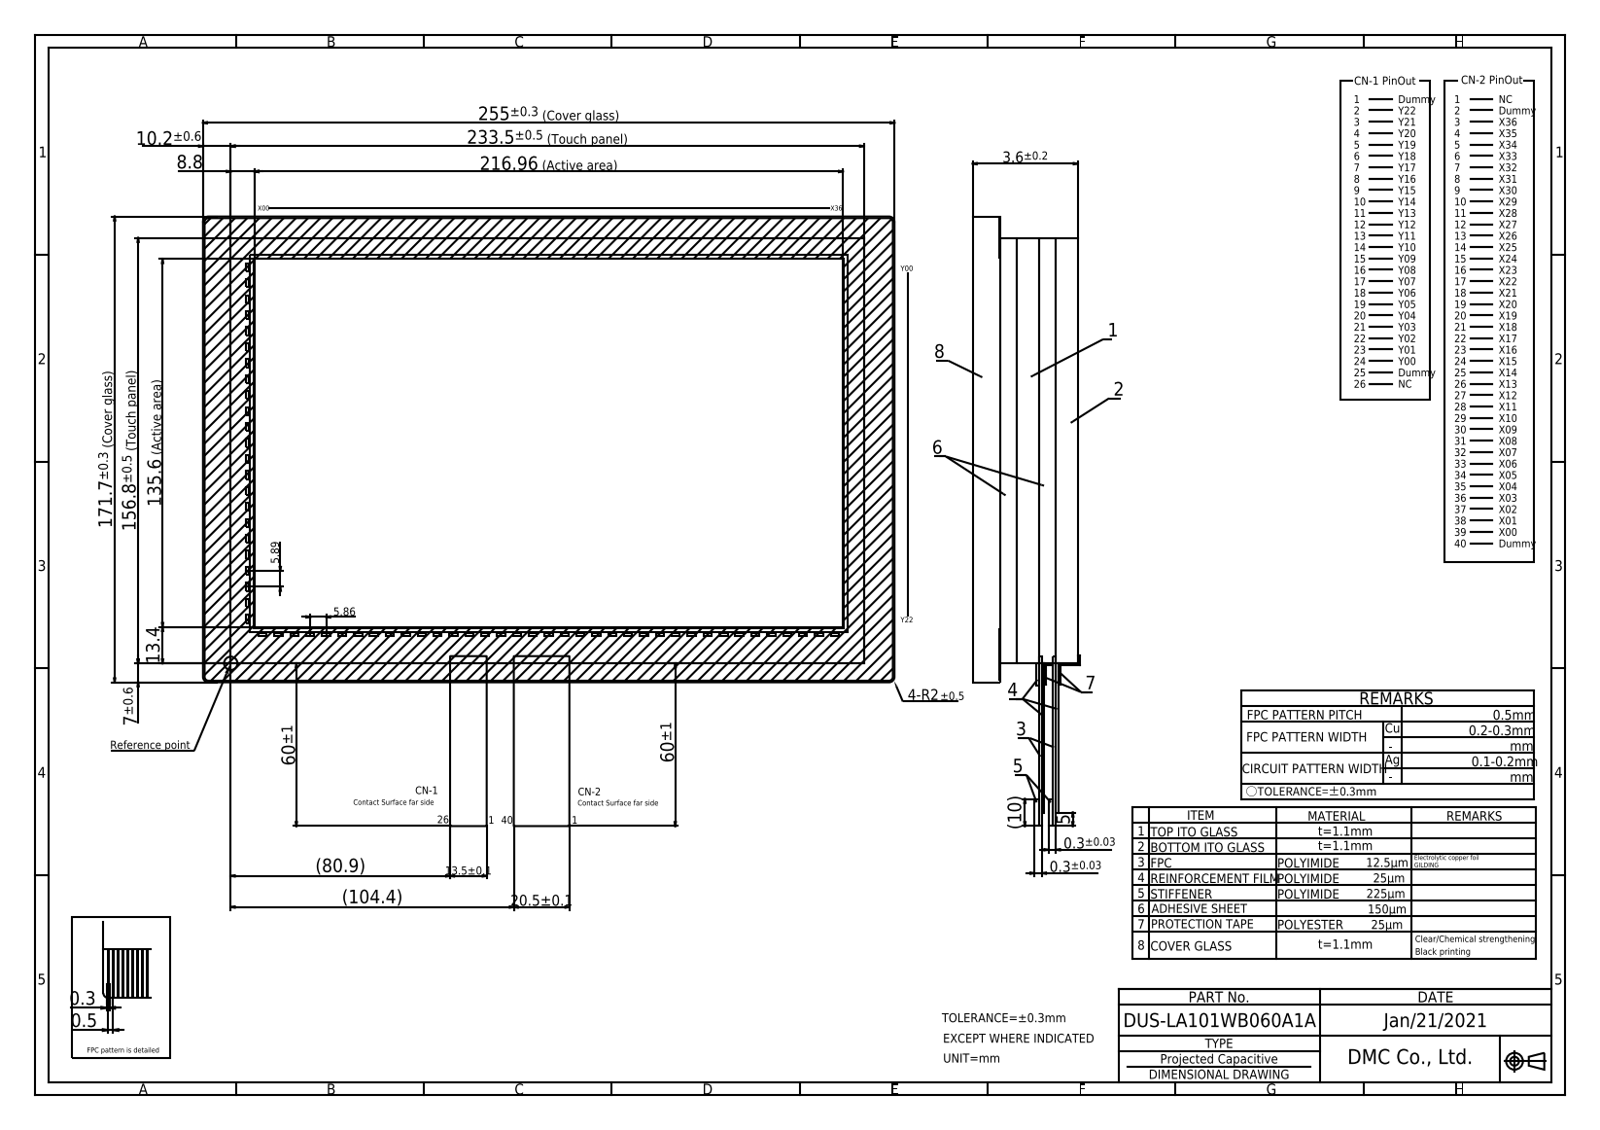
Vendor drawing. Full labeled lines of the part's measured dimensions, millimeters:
Part name (STEP PRODUCT): DUS-LA101WB060A1A
STEP written by: Autodesk Inventor 2020 (CONFIG_CONTROL_DESIGN)
Units: millimetres
Bodies: 1 solid, 308 faces (300 planar, 8 cylindrical, 0 other)
Overall size (bounding box): 357 × 259.04 × 3.6
Volume: 137 036 mm³ · Surface area: 153 497 mm²
Partial cylindrical surfaces — rounded edges, fillets, slot ends (radius × count): R0.2 ×4, R2 ×4
Main face-to-face distances: 3.6, 2.5, 1.1, 1.2, 2.4, 1.25, 1.15, 1.35, 2.45, 2.35
